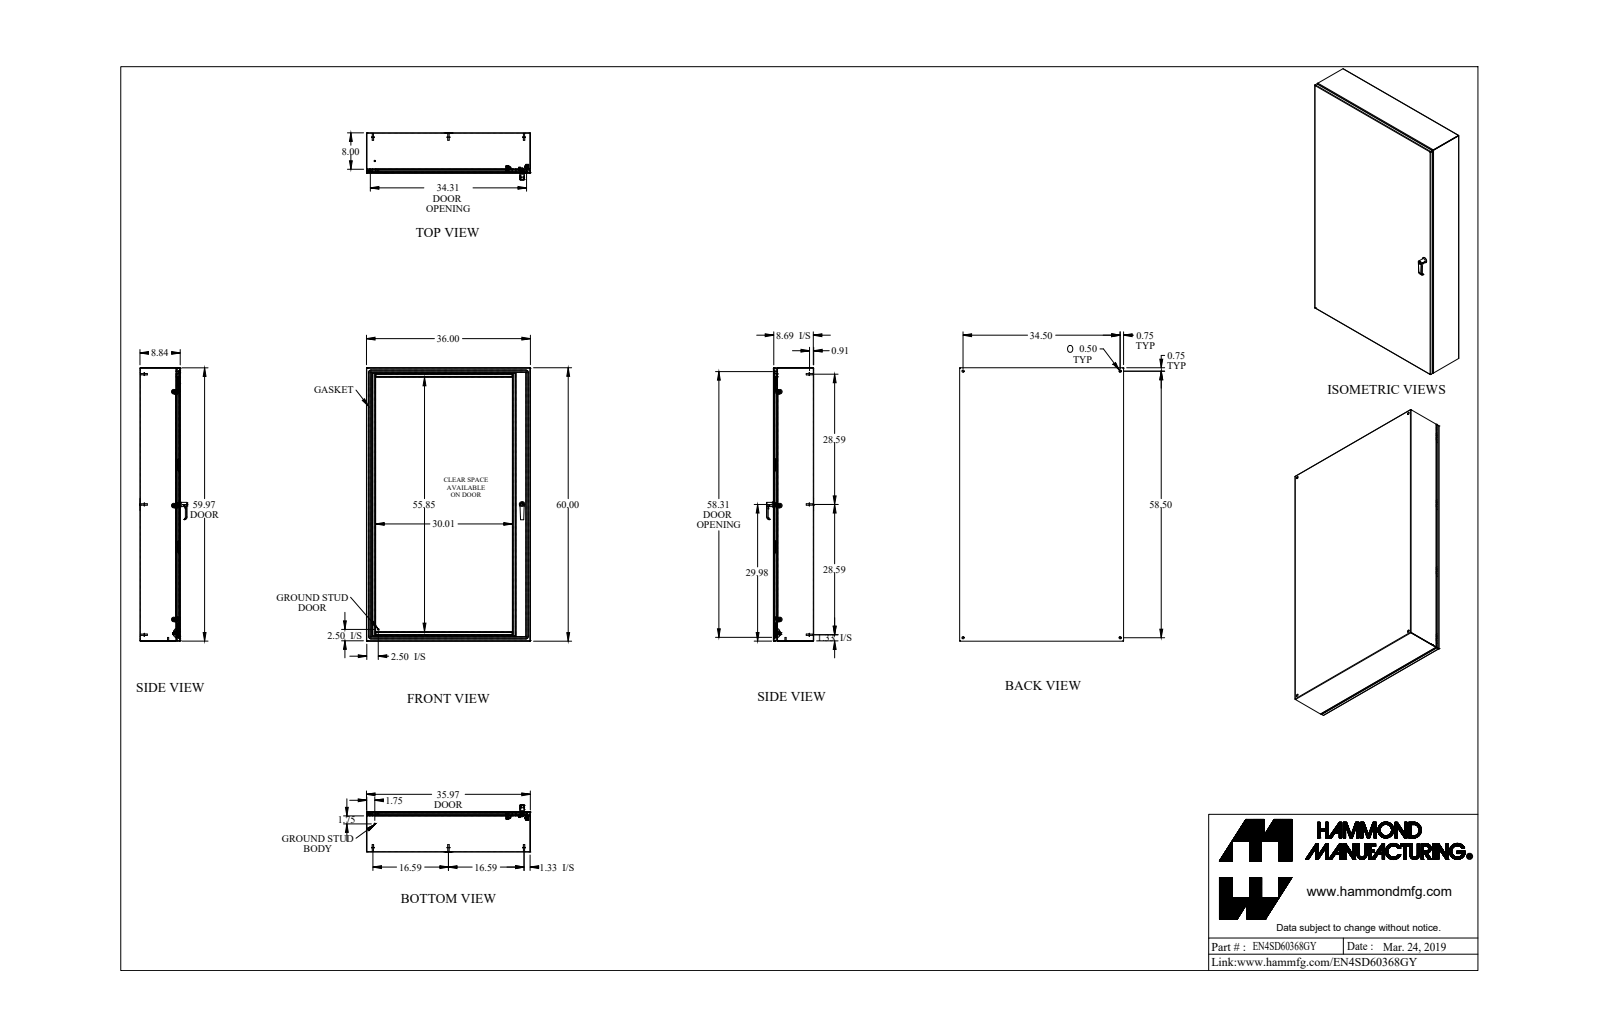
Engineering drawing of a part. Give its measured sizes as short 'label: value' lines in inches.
name: EN4SD60368GY_Default
written by: SolidWorks 2019 (CONFIG_CONTROL_DESIGN)
unit: in
bodies: 61 solids, 1731 faces (755 planar, 644 cylindrical, 332 other)
size: 60 × 36 × 10.367
volume: 497.4 in³; area: 14 037 in²
holes: 6× ⌀0.176, 4× ⌀0.196, 4× ⌀0.5, 3× ⌀0.25, 3× ⌀0.265, 3× ⌀0.413, 2× ⌀0.256, 2× ⌀0.313, 2× ⌀0.394, 1× ⌀0.172, 1× ⌀0.24, 1× ⌀0.242
bosses: 9× ⌀0.625, 8× ⌀0.313, 8× ⌀0.27, 8× ⌀0.25, 6× ⌀0.375, 6× ⌀0.156, 3× ⌀1, 2× ⌀0.63
rounds: 24× R0.043, 21× R0.062, 20× R0.036, 20× R0.108, 15× R0.03, 10× R0.094, 9× R0.016, 8× R0.006
face distances: 0.072, 8.765, 8.693, 8.837, 35.928, 59.928, 35.856, 36, 59.856, 60
hole spacings: 0.787, 24.981, 49.969, 4.398, 24.988, 25, 33.698, 34.5
